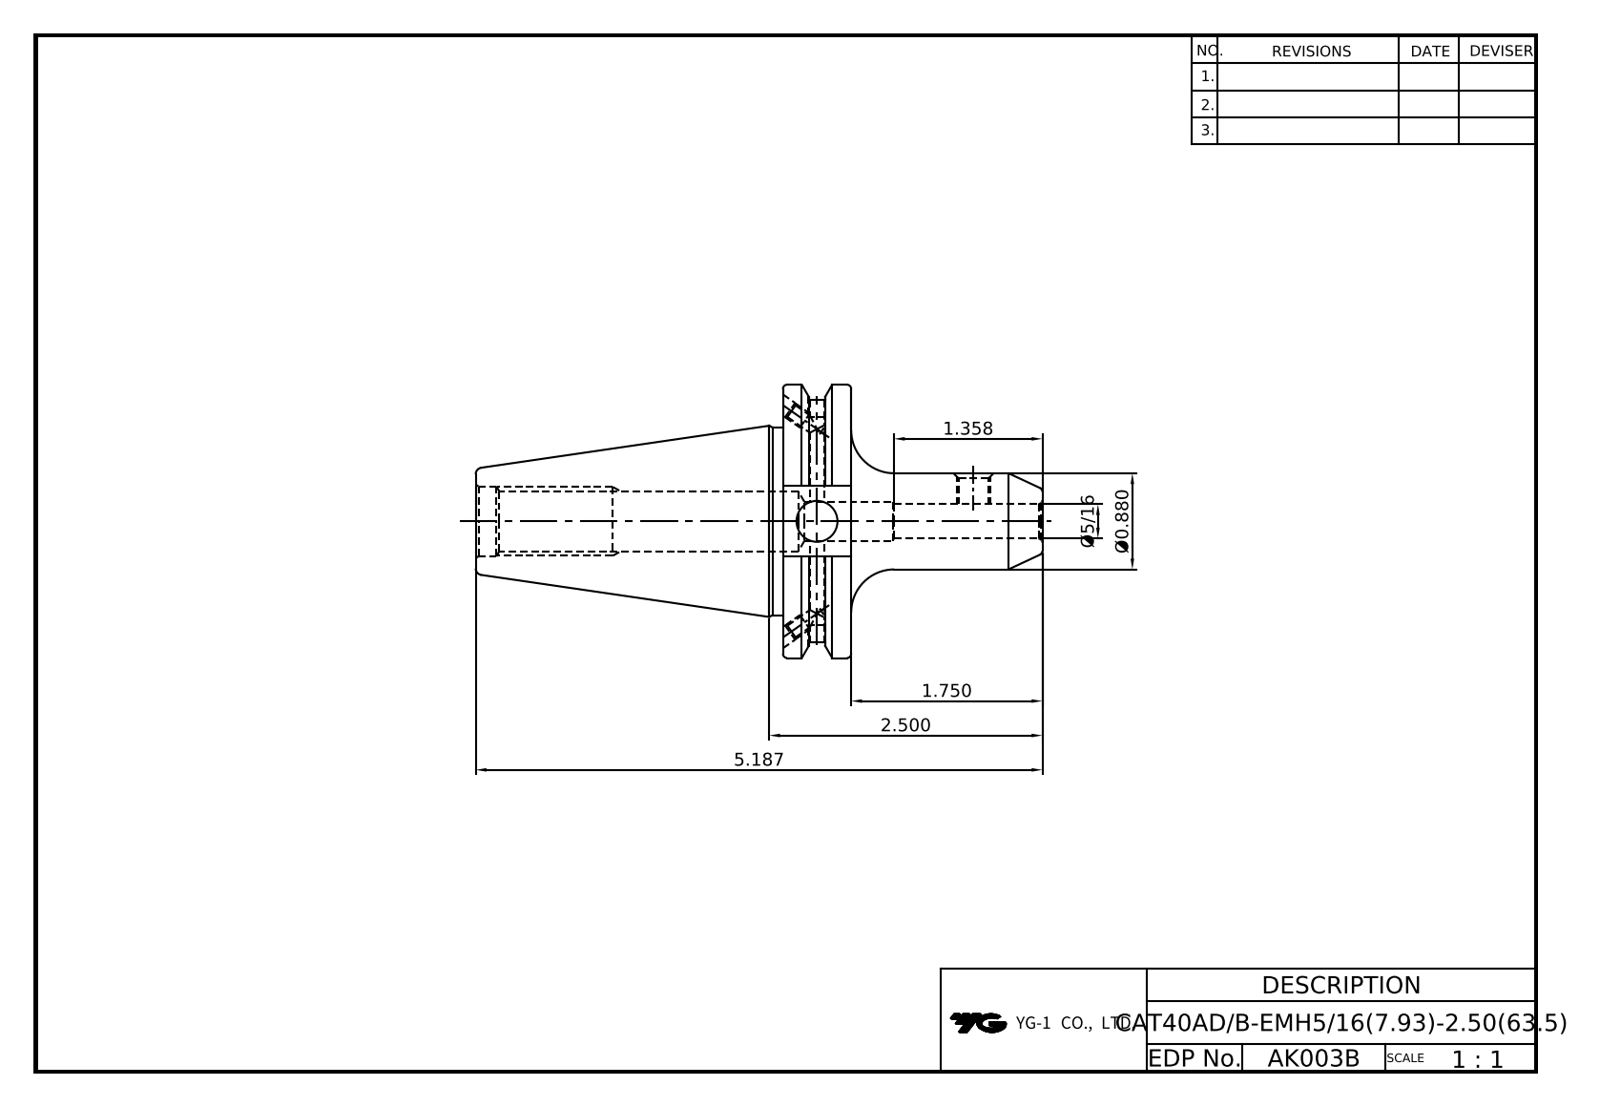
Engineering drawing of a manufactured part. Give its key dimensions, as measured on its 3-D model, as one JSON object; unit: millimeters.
{"part_name": "LO-CAT40ADB-EMH7.9375-63.5", "step_written_by": "Autodesk Inventor 2025 (AUTOMOTIVE_DESIGN)", "units": "millimeters", "bodies": {"solids": 1, "faces": 87, "planar": 35, "cylindrical": 28, "other": 24}, "overall_size": [131.75, 63.5, 61.09], "volume_mm3": 116476, "surface_area_mm2": 24734, "round_holes": [[3.24, 4], [4, 2], [4.2, 2], [6.78, 1], [7.94, 1], [9, 1], [9.53, 1], [13.39, 1], [16.3, 1]], "round_bosses_or_shafts": [[63.5, 1], [43.6, 1], [22.35, 1]], "partial_cylinders_radius": [[28.15, 1]], "face_to_face_distances": [15.88, 47.6, 16.38, 71.42, 87.3, 77.47, 6.05, 9.83, 81.3, 9.88]}
